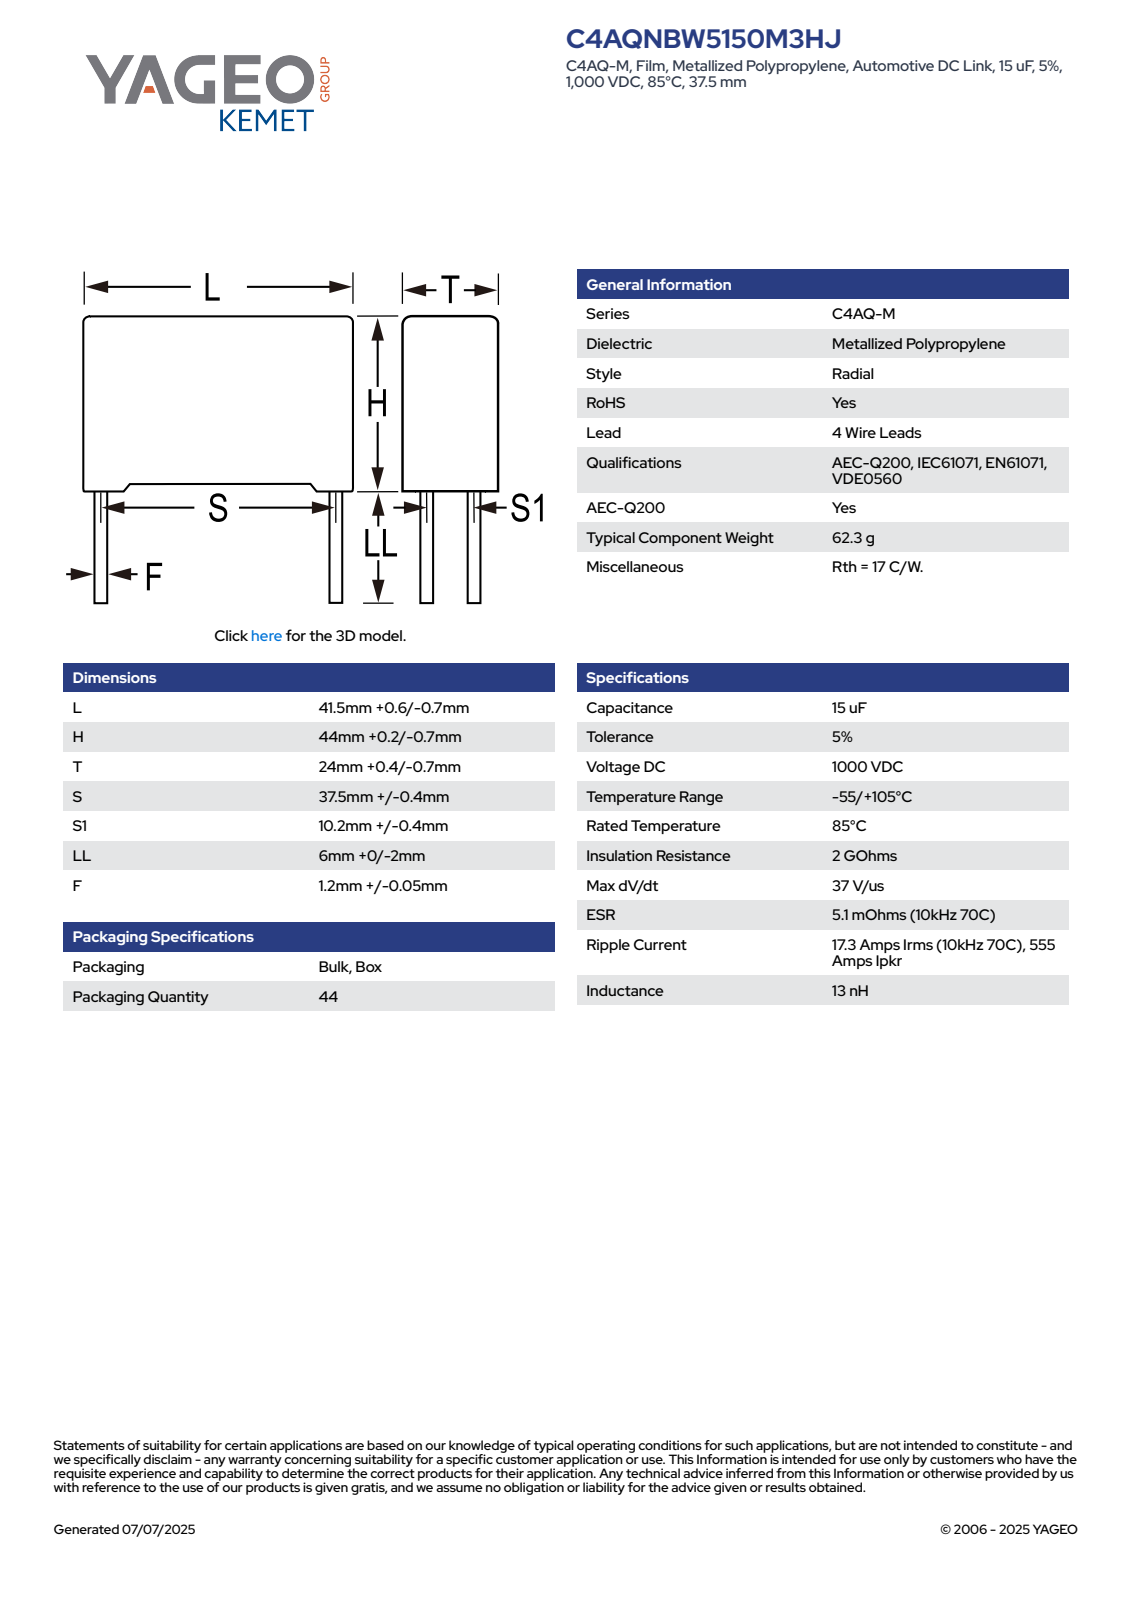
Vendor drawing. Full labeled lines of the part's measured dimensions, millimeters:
Part name (STEP PRODUCT): CFP_RB4_41.5X44X24_L42.1H44.2T24.4S37.5S110.2LL6F1.25
STEP written by: SolidWorks 2014 (AUTOMOTIVE_DESIGN)
Units: millimetres
Bodies: 4 solids, 87 faces (79 planar, 8 cylindrical, 0 other)
Overall size (bounding box): 50.2 × 42.1 × 24.41
Volume: 44 244 mm³ · Surface area: 8 179 mm²
Round bosses / shafts (diameter × count): ⌀1.25 ×4
Main face-to-face distances: 24.4, 42.1, 42.9, 1.3, 44.2, 1.5, 24.41, 40.6, 22.9, 39.1
